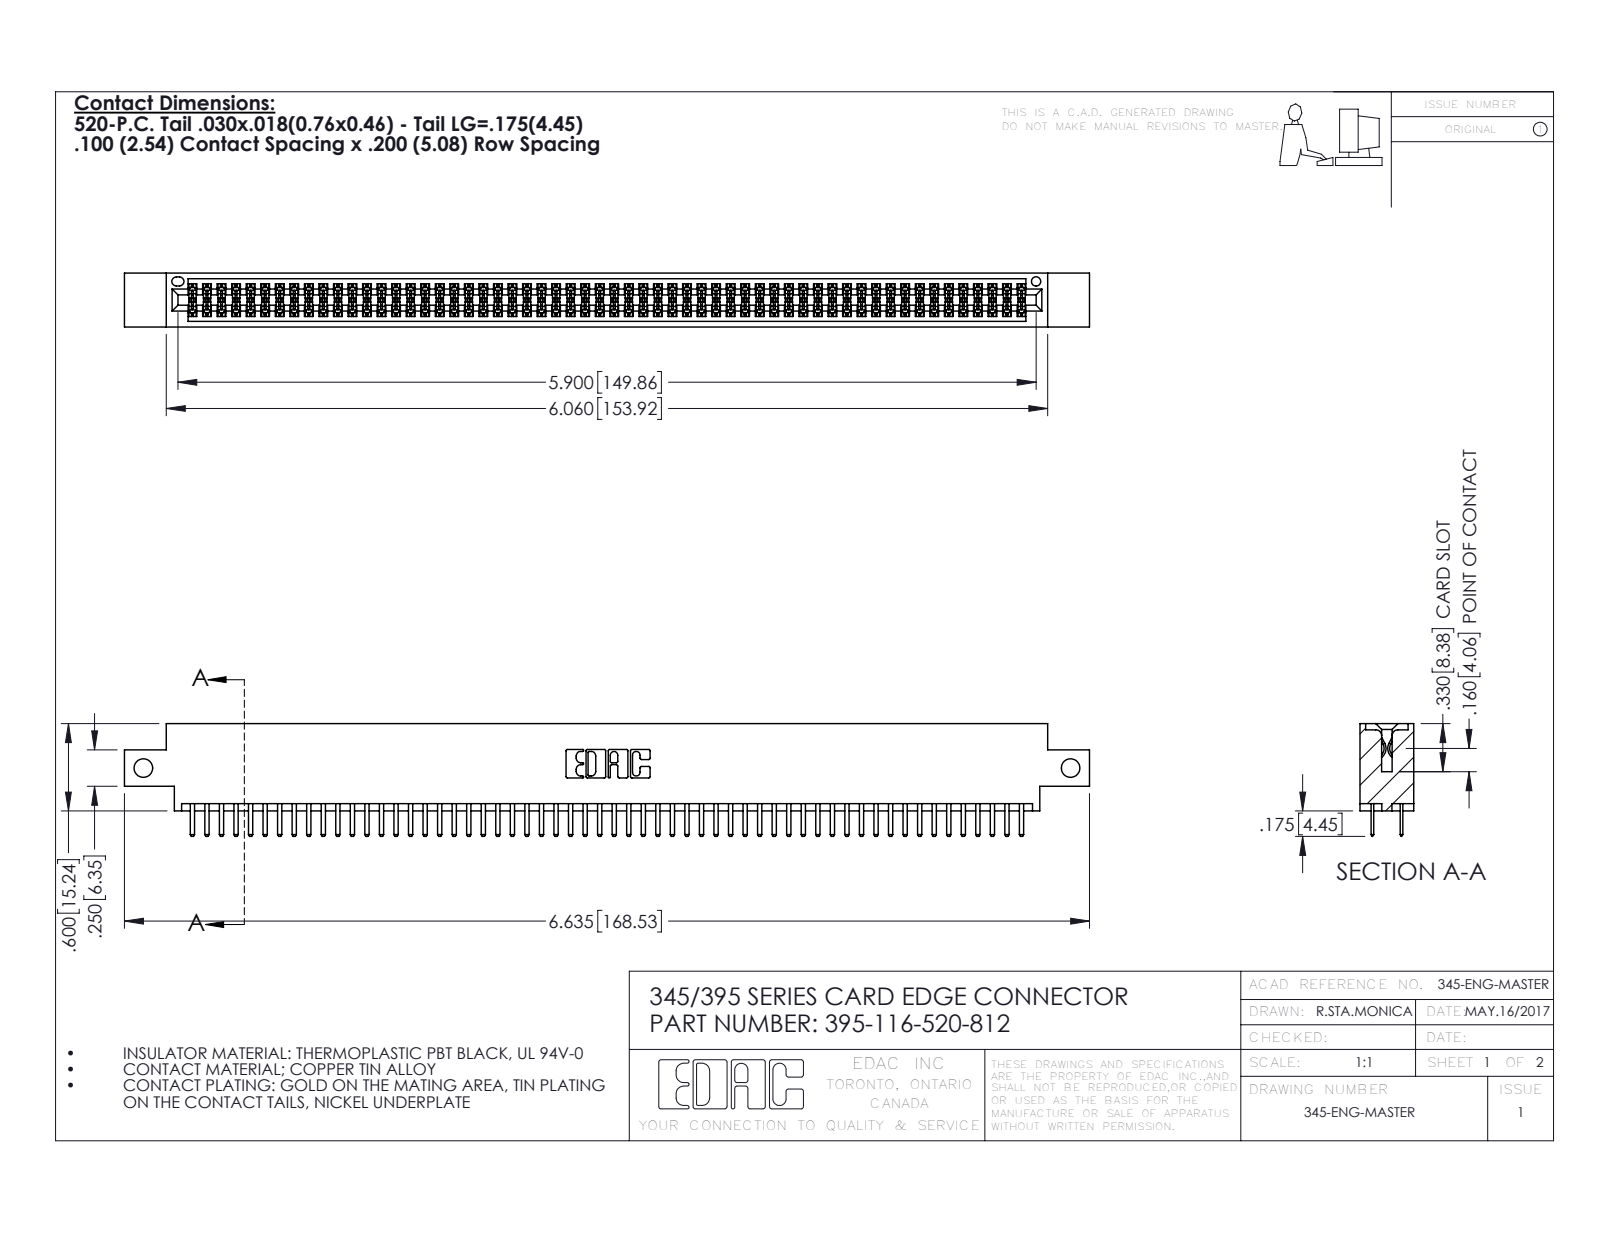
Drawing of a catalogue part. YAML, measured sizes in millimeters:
part_name: "395-116-520-812; 345-292-001_345-293-120; 345 Part_0.170 Offset - Side Mount"
step_written_by: "SolidWorks 2016 (CONFIG_CONTROL_DESIGN)"
units: millimeters
bodies: {solids: 117, faces: 6394, planar: 4144, cylindrical: 2250, other: 0}
overall_size: [168.5, 19.7, 9.4]
volume: 16300
surface_area: 24260
round_holes:
  - {diameter: 3.3, count: 2}
  - {diameter: 1.6, count: 1}
partial_cylinders:
  - {radius: 0.2, count: 174}
  - {radius: 0.3, count: 120}
  - {radius: 0.3, count: 22}
  - {radius: 0.2, count: 6}
  - {radius: 0.8, count: 6}
  - {radius: 0.7, count: 3}
  - {radius: 0.4, count: 2}
  - {radius: 0.5, count: 2}
face_to_face_distances: [7.6, 1.8, 5.1, 9.4, 2.5, 6.9, 0.6, 5.7, 0.6, 1.8]
hole_center_spacings: [161.9]
